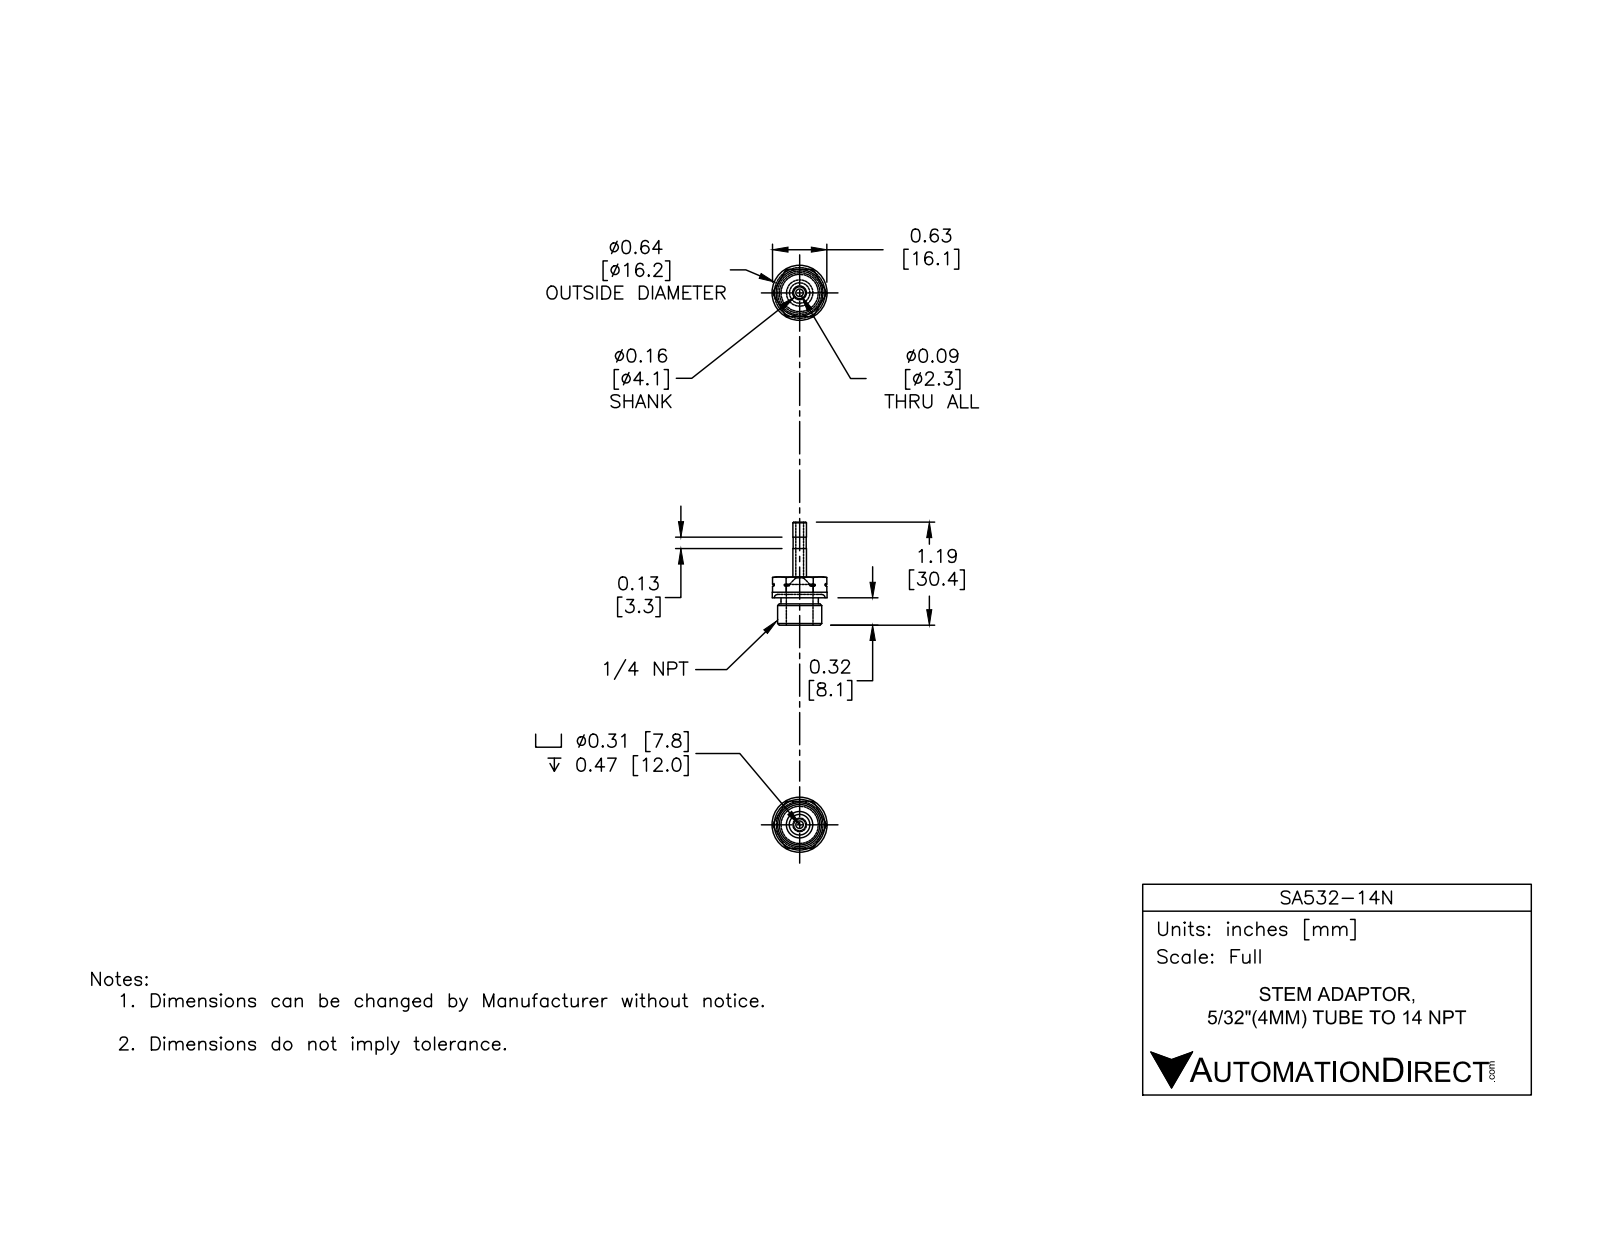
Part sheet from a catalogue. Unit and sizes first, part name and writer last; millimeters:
Units: millimetres
Overall size (bounding box): 30.35 × 16.2 × 16.2
Round holes (diameter × count): ⌀2.26 ×1, ⌀7.8 ×1
Round bosses / shafts (diameter × count): ⌀16.2 ×1, ⌀13 ×1, ⌀11 ×1, ⌀4.06 ×1, ⌀3.83 ×1
Partial cylindrical surfaces — rounded edges, fillets, slot ends (radius × count): R7.59 ×1
Main face-to-face distances: 6.12, 13.9, 8.05, 14.17, 9.67, 1.62, 4.5, 12, 3.95, 2.33
Volume: 1 742 mm³ · Surface area: 1 954 mm²
Bodies: 2 solids, 66 faces (15 planar, 23 cylindrical, 28 other)
Part name (STEP PRODUCT): SA532-14N
STEP written by: SolidWorks 2015 (CONFIG_CONTROL_DESIGN)
